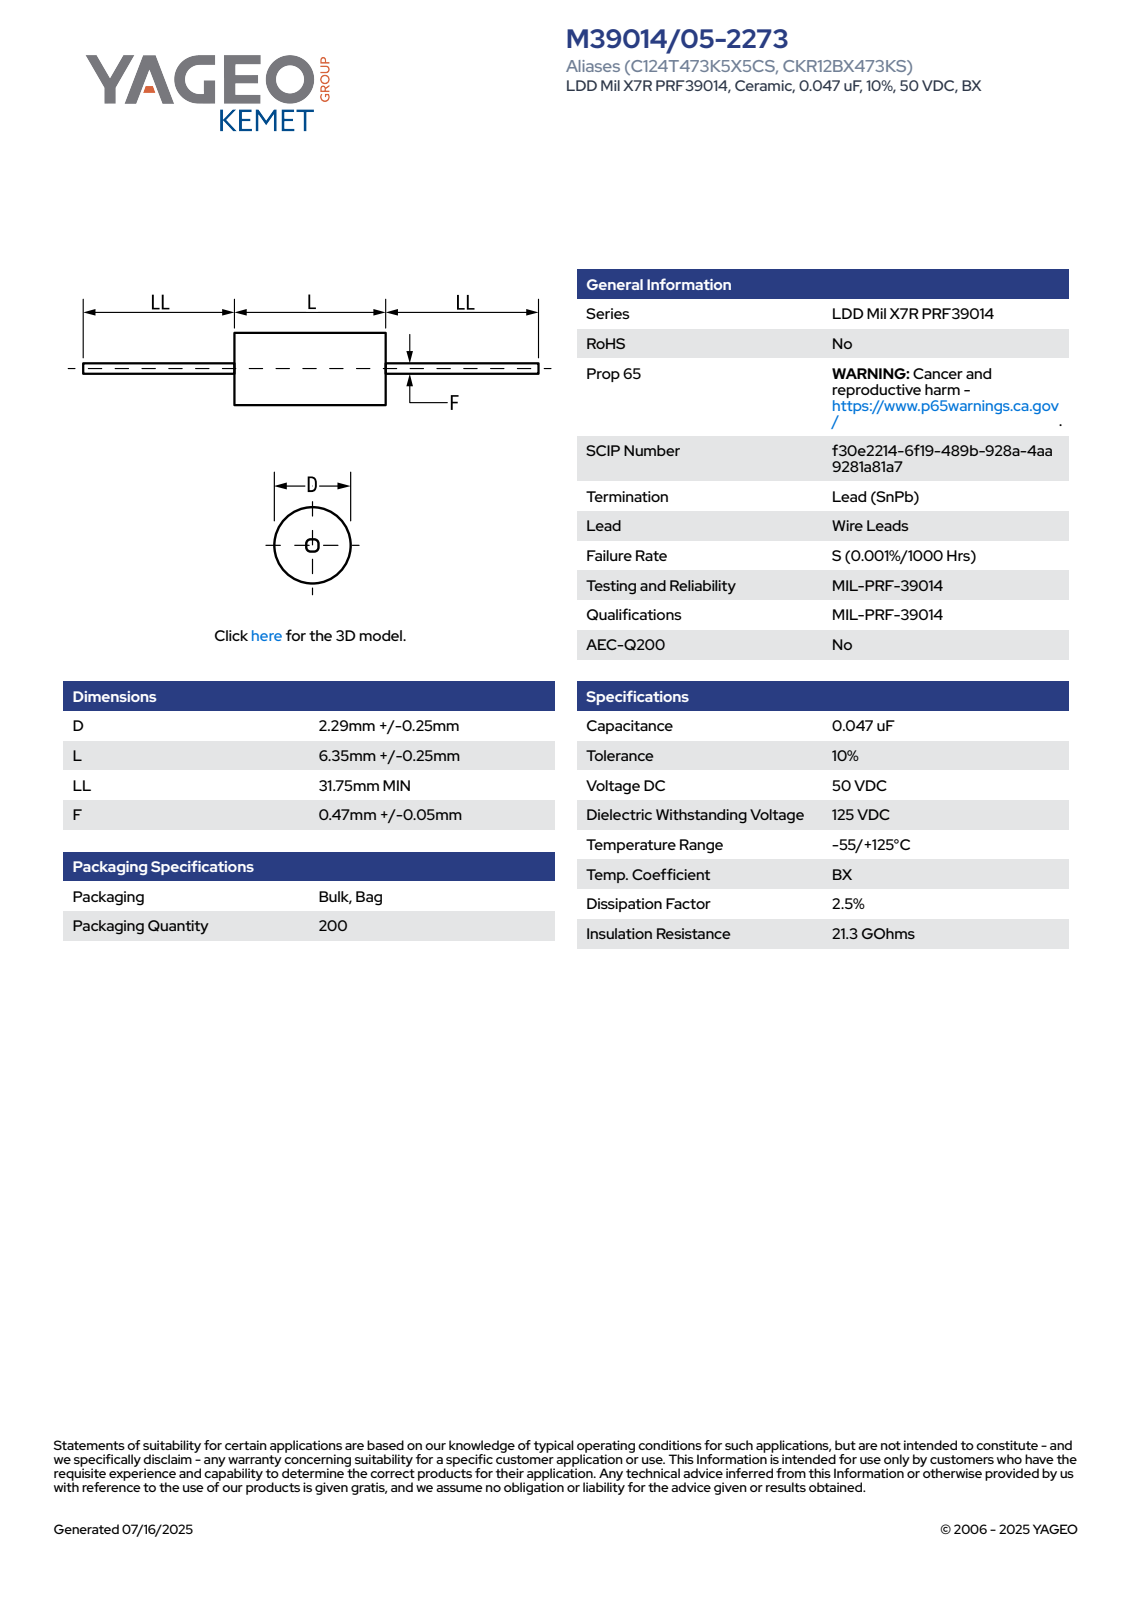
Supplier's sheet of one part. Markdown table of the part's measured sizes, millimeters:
| quantity | value |
| --- | --- |
| part name | CCA_AXM_C124_D2.54L6.6LL31.75F0.52 |
| STEP written by | SolidWorks 2021 (AUTOMOTIVE_DESIGN) |
| units | millimeters |
| bodies | 1 solid, 66 faces (26 planar, 9 cylindrical, 31 other) |
| overall size | 70.1 × 2.54 × 2.54 |
| volume | 47 mm³ |
| surface area | 167 mm² |
| round bosses / shafts (diameter × count) | 2.54 × 1, 0.52 × 1 |
| partial cylindrical surfaces (radius × count) | 1.26 × 1 |
| main face-to-face distances | 6.6, 31.75, 38.35, 70.1 |
